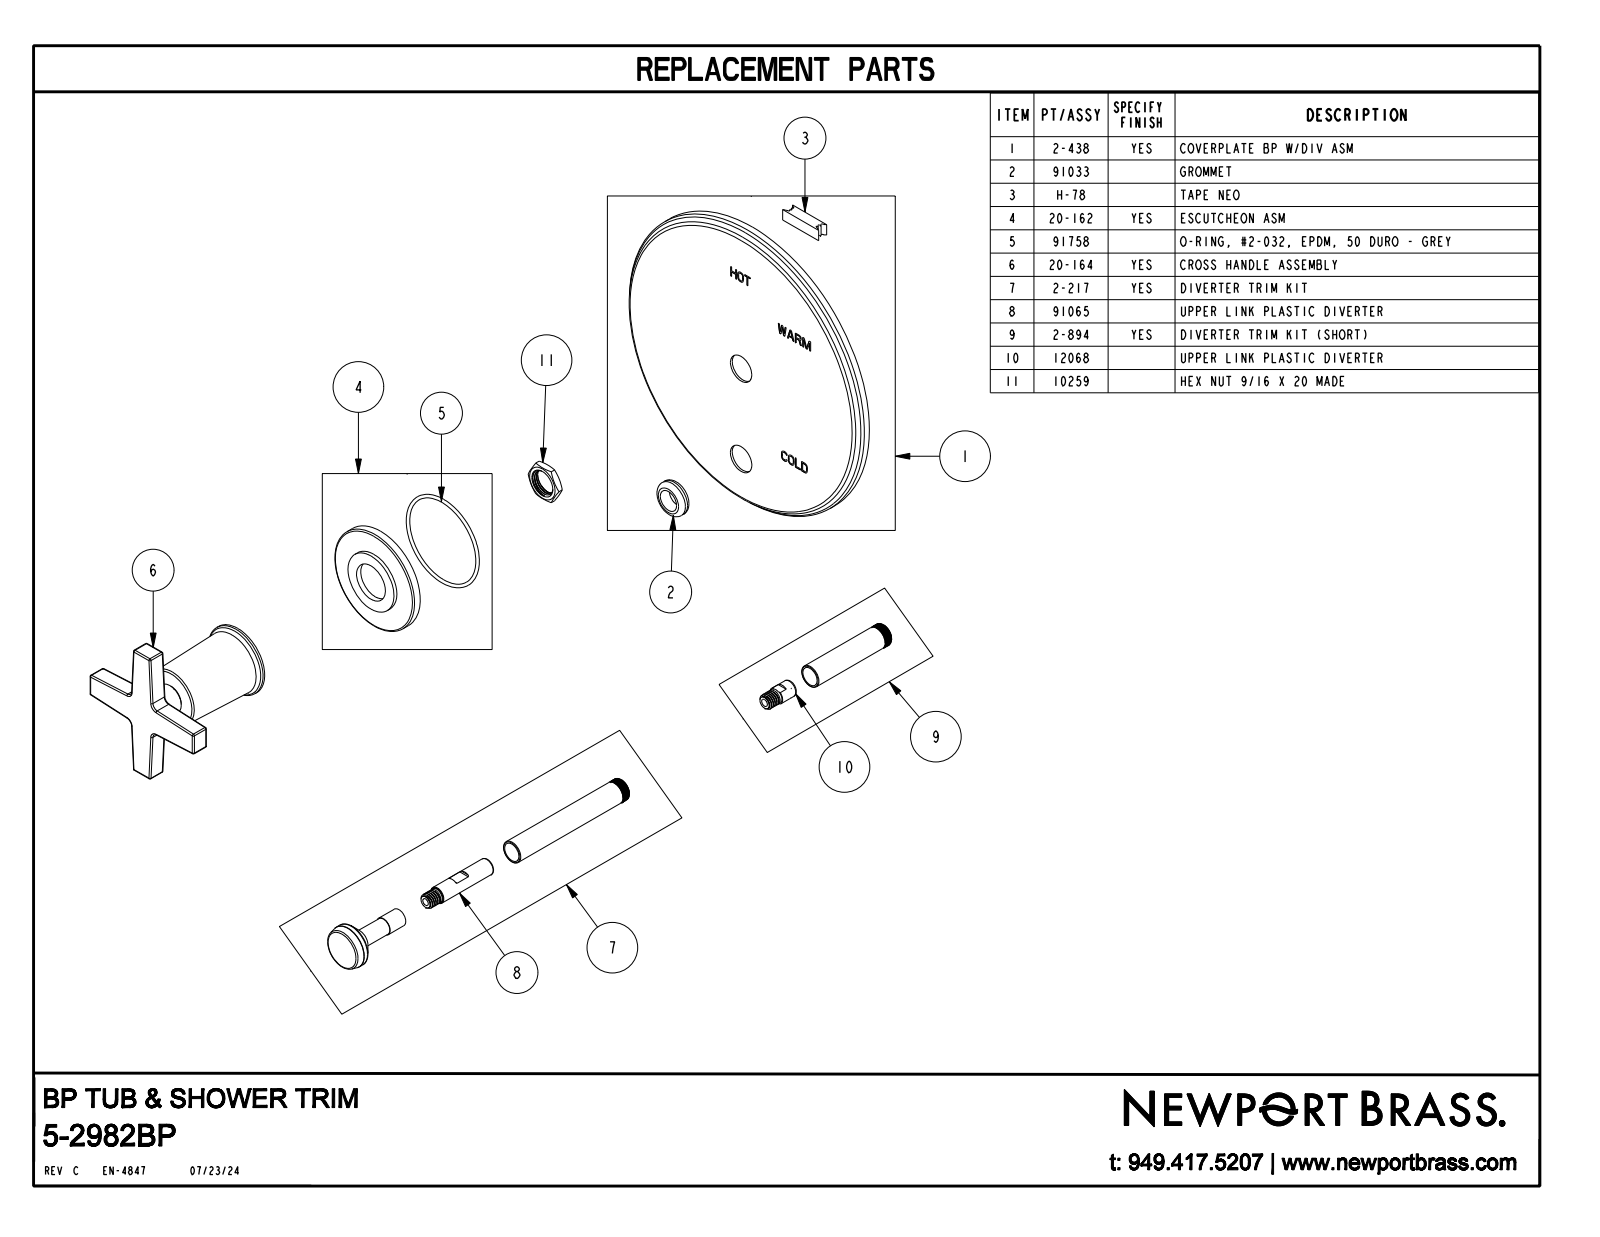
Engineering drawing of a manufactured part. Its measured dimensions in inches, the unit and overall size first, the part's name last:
Units: inches
Overall size (bounding box): 6.5 × 6.5 × 3.183
Round bosses / shafts (diameter × count): ⌀6.5 ×1, ⌀2.2 ×1, ⌀1.5 ×1, ⌀1.275 ×1, ⌀0.9 ×1, ⌀0.625 ×1, ⌀0.525 ×1, ⌀0.472 ×1
Partial cylindrical surfaces — rounded edges, fillets, slot ends (radius × count): R0.03 ×32, R0.125 ×4
Main face-to-face distances: 0.313, 3.183, 2.87, 0.187, 0.5, 2.683, 2.808, 2.495, 2.308, 0.375
Volume: 14.84 in³ · Surface area: 92.83 in²
Bodies: 1 solid, 393 faces (283 planar, 54 cylindrical, 56 other)
Part name (STEP PRODUCT): 5-2982BP
STEP written by: CREO PARAMETRIC BY PTC INC, 2018400 (CONFIG_CONTROL_DESIGN)
